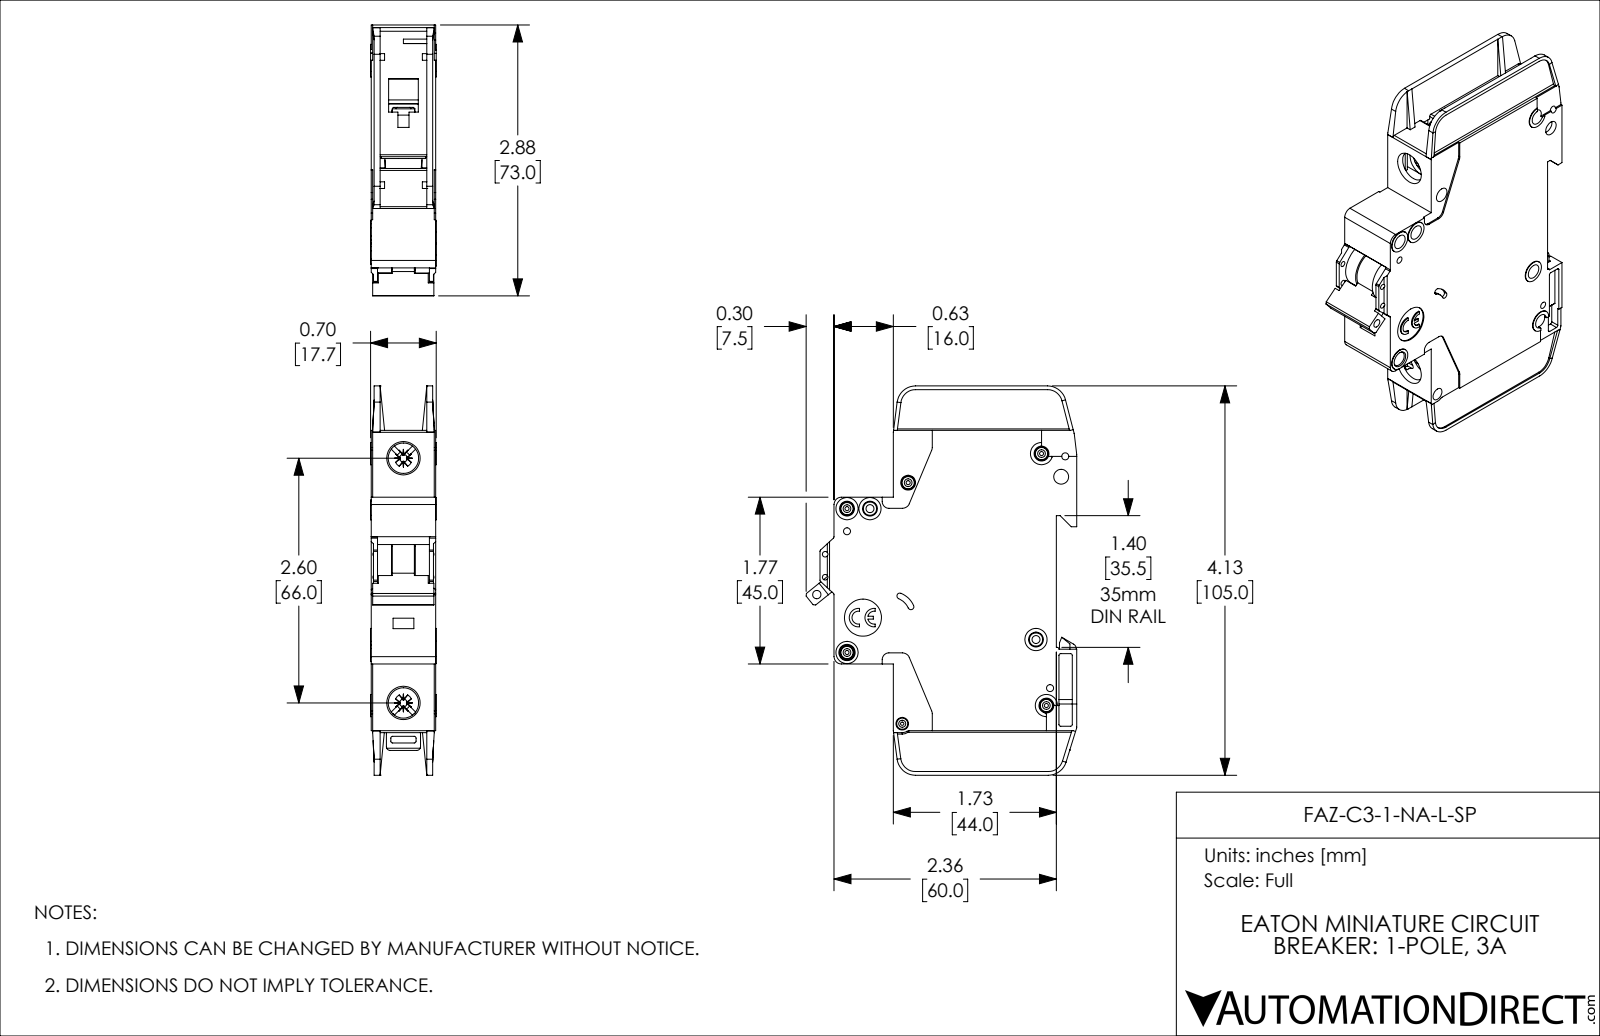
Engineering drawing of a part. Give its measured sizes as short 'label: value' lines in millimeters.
name: FAZ-C3-1-NA-L-SP
written by: SolidWorks 2019 (AUTOMOTIVE_DESIGN)
unit: mm
bodies: 1 solid, 1127 faces (671 planar, 357 cylindrical, 99 other)
size: 105 × 73.1 × 17.7
volume: 76 720 mm³; area: 26 460 mm²
holes: 8× ⌀4, 5× ⌀1.1, 4× ⌀1.9, 2× ⌀1.5, 2× ⌀2.2, 2× ⌀8.2, 1× ⌀0.9, 1× ⌀2.3, 1× ⌀2.5, 1× ⌀3.4, 1× ⌀10
bosses: 5× ⌀3.3, 4× ⌀6, 2× ⌀3, 1× ⌀2.5
rounds: 42× R0.5, 10× R0.4, 10× R1, 8× R2, 5× R5, 4× R0.2, 4× R0.7, 4× R1.1
face distances: 1.2, 17.4, 15, 16.2, 2.4, 13.8, 0.4, 0.8, 12.6, 14.6
hole spacings: 6.2, 13.6, 22.1, 4.8, 5.1, 5.2, 5.6, 6.1
